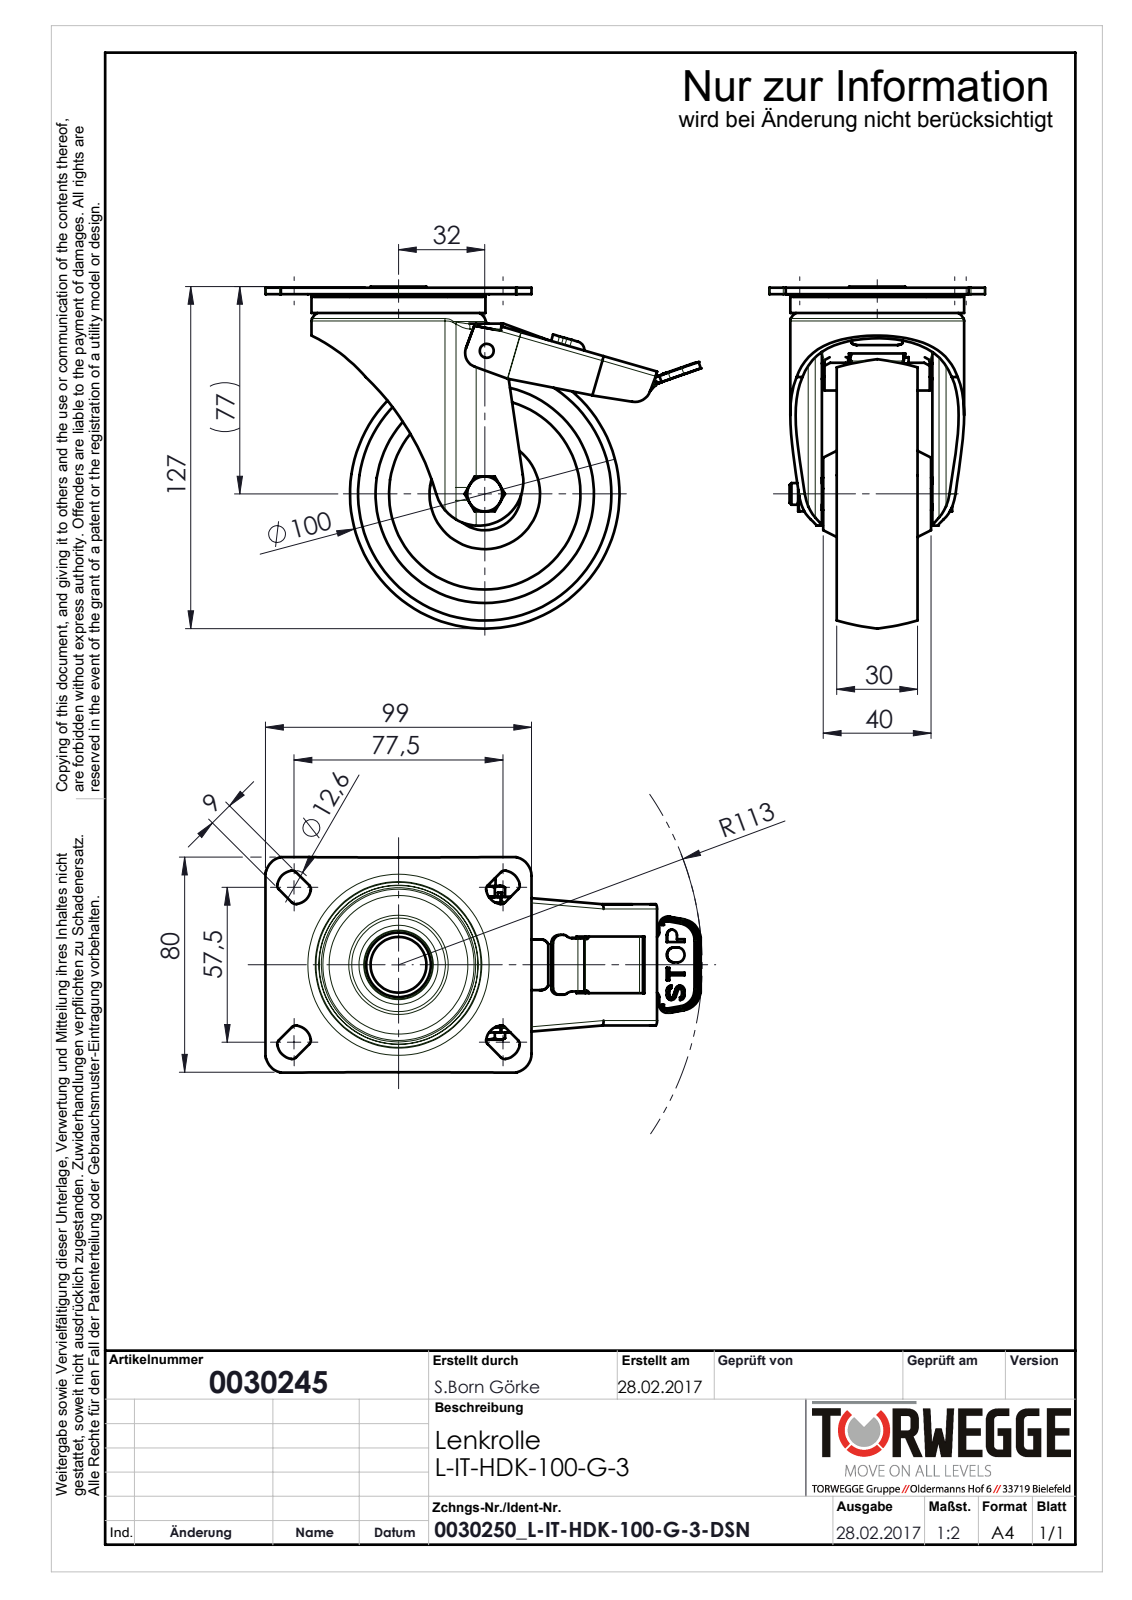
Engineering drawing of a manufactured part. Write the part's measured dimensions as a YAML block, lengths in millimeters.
part_name: "0030250_L-IT-HDK-100-G-3-DSN"
step_written_by: "SolidWorks 2016 (AUTOMOTIVE_DESIGN)"
units: millimeters
bodies: {solids: 0, faces: 455, planar: 192, cylindrical: 117, other: 146}
overall_size: [161.52, 127, 80]
round_holes:
  - {diameter: 5.2, count: 1}
  - {diameter: 6.8, count: 1}
  - {diameter: 8, count: 1}
  - {diameter: 8.39, count: 1}
  - {diameter: 10, count: 1}
  - {diameter: 12, count: 1}
  - {diameter: 13, count: 1}
  - {diameter: 24, count: 1}
  - {diameter: 36.4, count: 1}
  - {diameter: 58.15, count: 1}
  - {diameter: 67.26, count: 1}
round_bosses_or_shafts:
  - {diameter: 64.5, count: 1}
  - {diameter: 13.6, count: 1}
  - {diameter: 13.5, count: 1}
  - {diameter: 13, count: 1}
  - {diameter: 9.99, count: 1}
partial_cylinders:
  - {radius: 2, count: 20}
  - {radius: 1.8, count: 6}
  - {radius: 0.5, count: 4}
  - {radius: 1, count: 4}
  - {radius: 6.3, count: 4}
  - {radius: 7.12, count: 4}
  - {radius: 1.8, count: 2}
  - {radius: 2, count: 2}
face_to_face_distances: [2, 2.45, 9, 21, 12, 16.5, 7.5, 28.5, 37.5, 4.96]
hole_center_spacings: [53.15]
